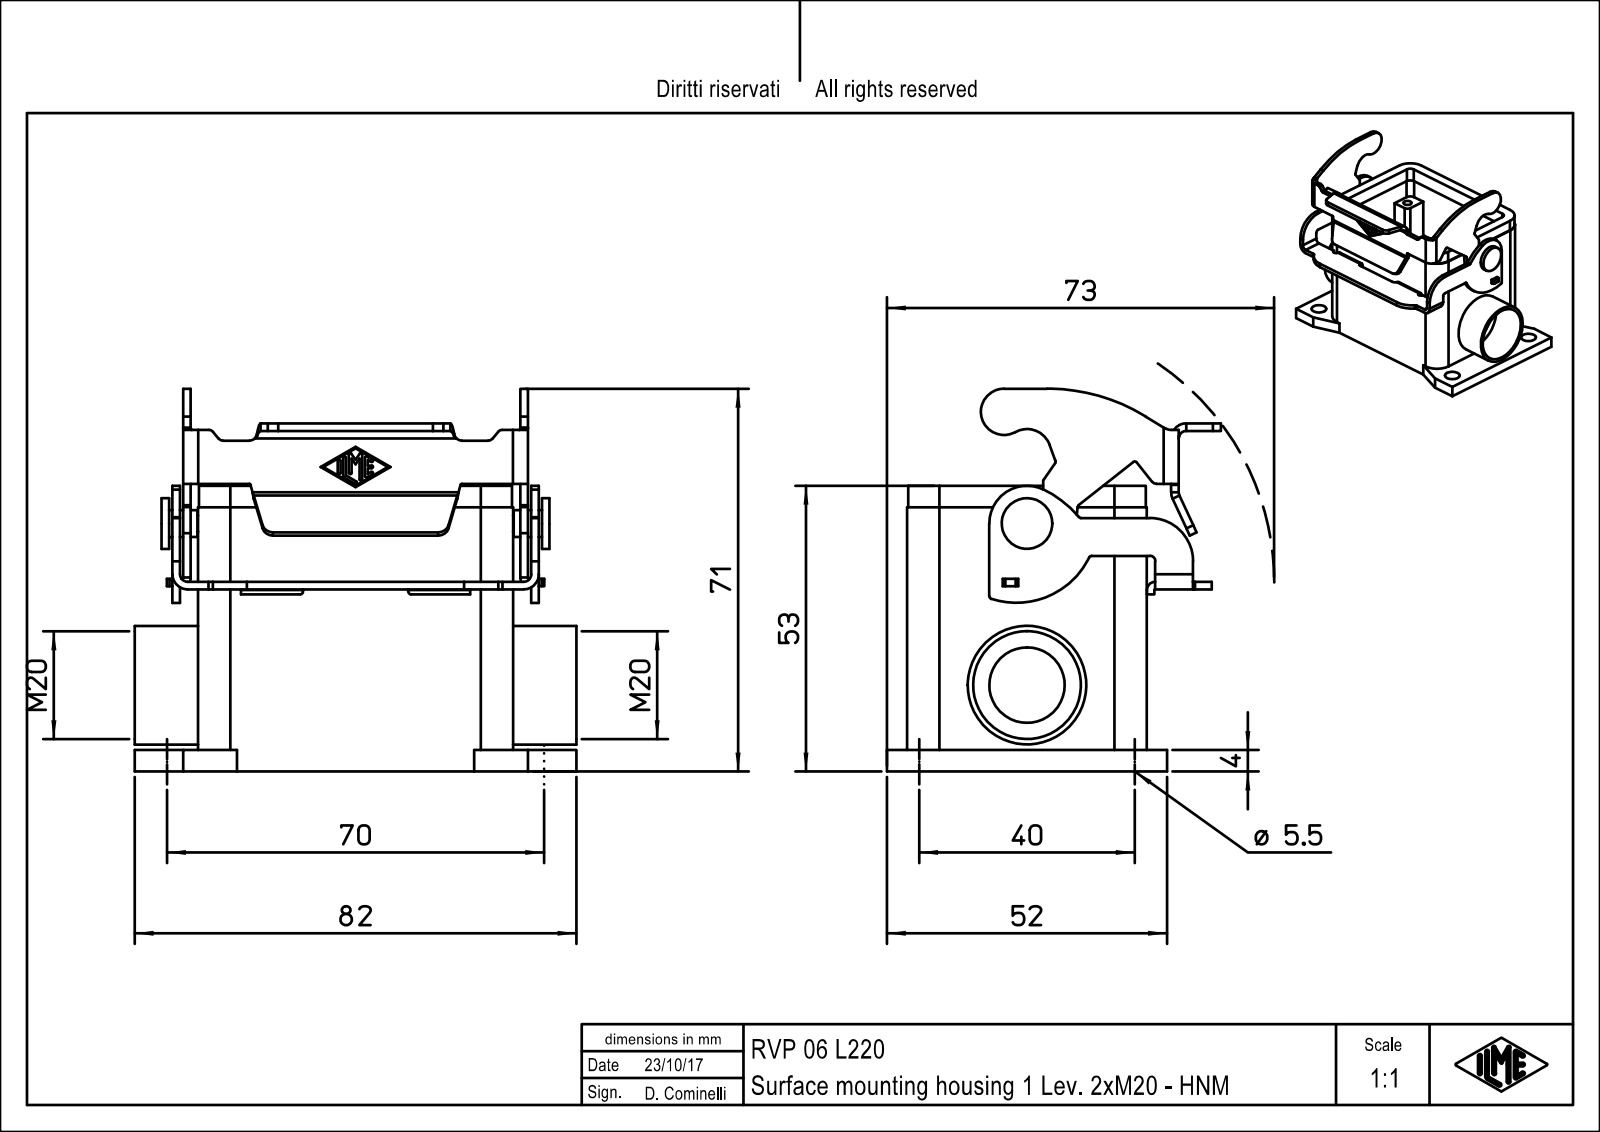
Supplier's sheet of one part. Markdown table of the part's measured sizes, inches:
| quantity | value |
| --- | --- |
| part name | RVP_06_L220 |
| STEP written by | PTC Creo Elements/Direct Modeling 19.0E 27-Jun-2016 (C) Parametric Technology GmbH (AUTOMOTIVE_DESIGN) |
| units | inches |
| bodies | 1 solid, 380 faces (198 planar, 170 cylindrical, 12 other) |
| overall size | 3.228 × 2.795 × 2.44 |
| volume | 4.23 in³ |
| surface area | 61.31 in² |
| round holes (diameter × count) | 0.097 × 4, 0.118 × 4, 0.217 × 4, 0.551 × 1, 0.787 × 1 |
| round bosses / shafts (diameter × count) | 0.866 × 1, 0.37 × 1, 0.197 × 1, 0.118 × 1 |
| partial cylindrical surfaces (radius × count) | 0.01 × 16, 0.02 × 12, 0.039 × 12, 0.059 × 11, 0.079 × 8, 0.055 × 6, 0.11 × 6, 0.071 × 4 |
| main face-to-face distances | 0.157, 0.055, 1.594, 1.752, 0.079, 2.543, 0.266, 1.437, 1.988, 0.423 |
| hole center spacings | 0.572, 1.415, 2.259, 2.603, 1.063, 1.575, 1.732, 2.032 |
